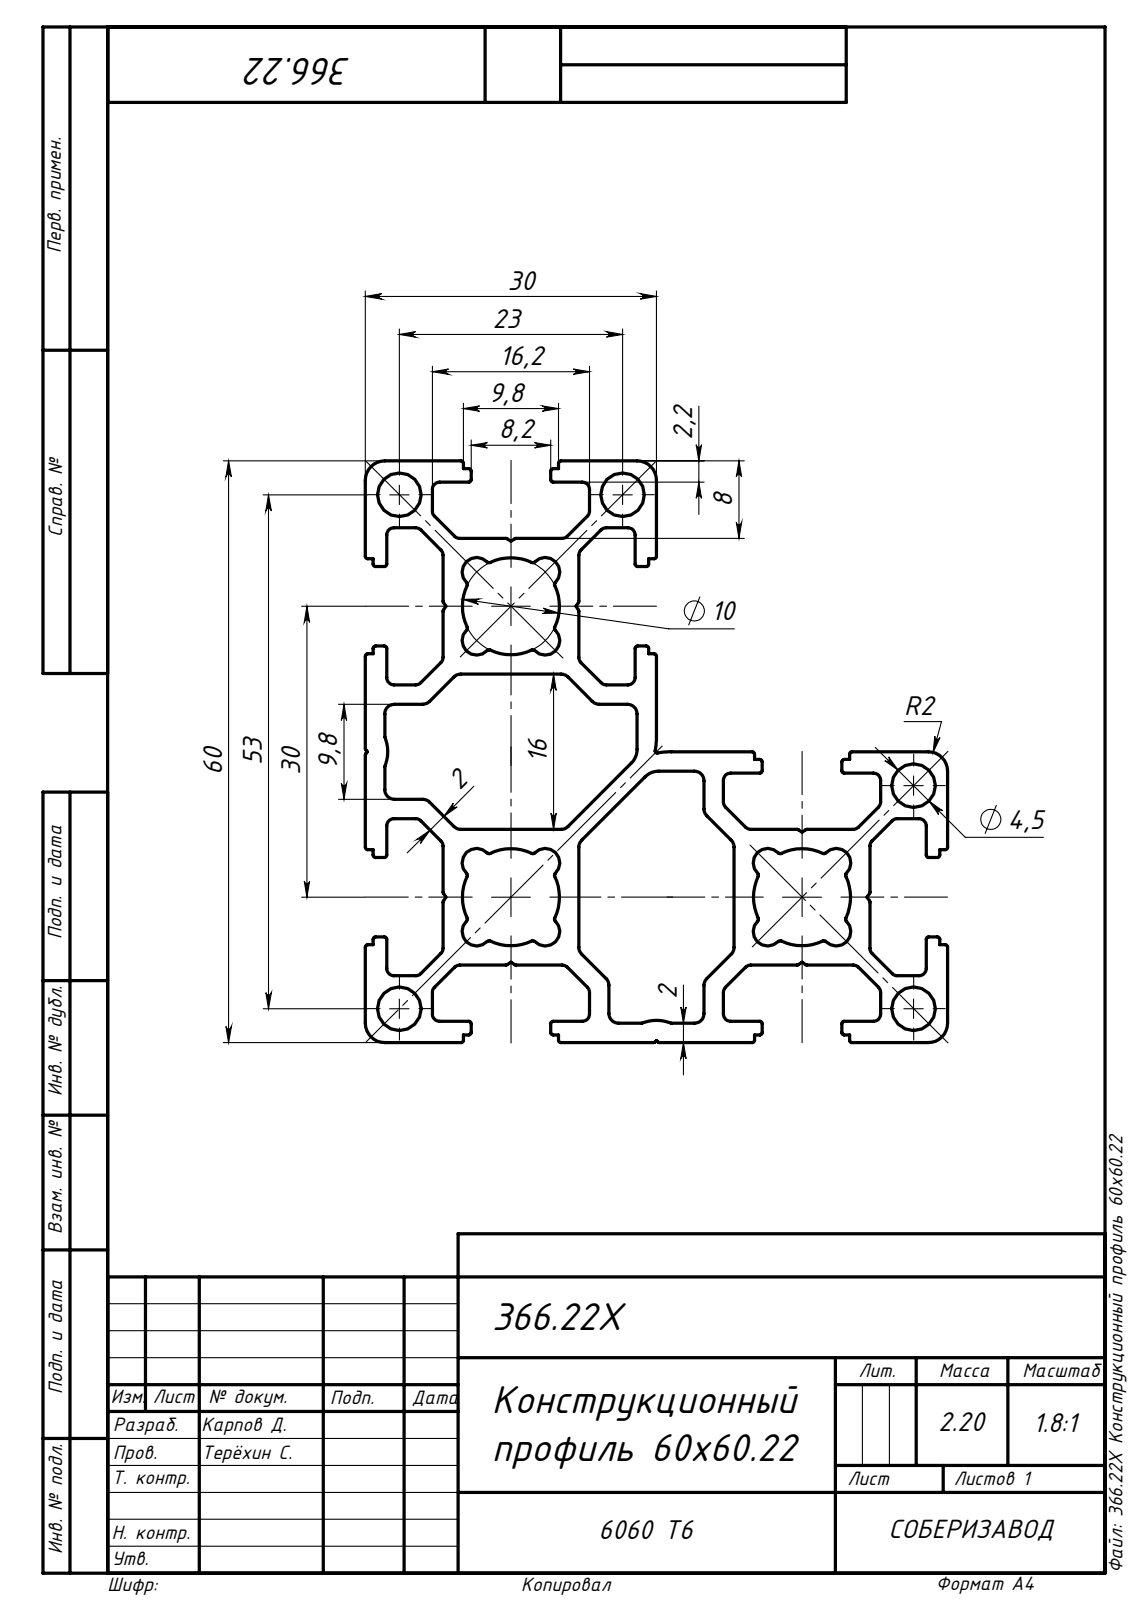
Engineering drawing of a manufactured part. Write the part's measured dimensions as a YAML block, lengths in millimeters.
part_name: "366.22X Конструкционный профиль 60х60.22"
step_written_by: "SolidWorks 2019 (AUTOMOTIVE_DESIGN)"
units: millimeters
bodies: {solids: 1, faces: 399, planar: 178, cylindrical: 221, other: 0}
overall_size: [1000, 60, 60]
volume: 814700
surface_area: 794811
round_holes:
  - {diameter: 4.5, count: 5}
partial_cylinders:
  - {radius: 0.25, count: 92}
  - {radius: 0.75, count: 48}
  - {radius: 1, count: 20}
  - {radius: 1.5, count: 12}
  - {radius: 2, count: 7}
  - {radius: 5, count: 3}
  - {radius: 4, count: 2}
  - {radius: 8, count: 2}
face_to_face_distances: [30, 22, 8, 2, 14, 38, 52, 2.2, 27.8, 5.8]
hole_center_spacings: [23, 53, 57.78, 60.9, 42.43, 74.95]
